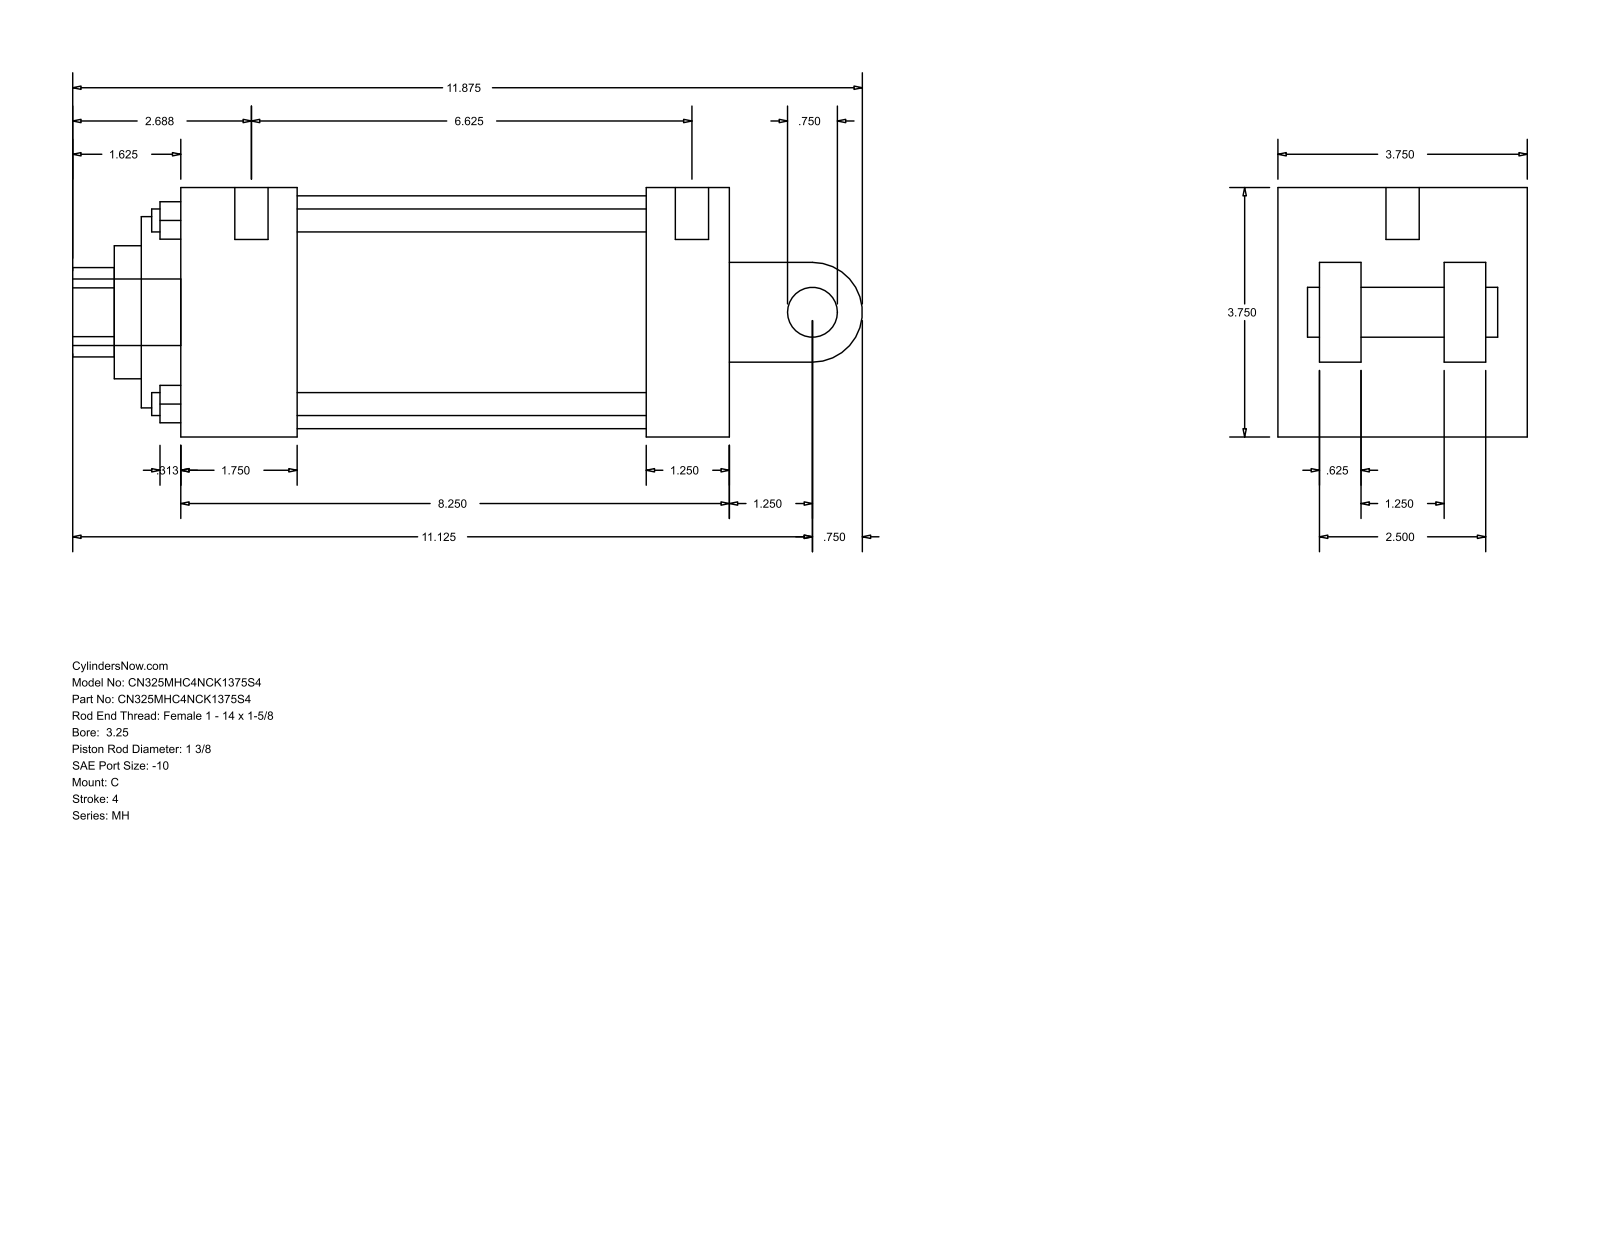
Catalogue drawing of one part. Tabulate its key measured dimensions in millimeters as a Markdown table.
| quantity | value |
| --- | --- |
| part name | MH_C__0325_1.375 |
| STEP written by | GSSL Pune (CONFIG_CONTROL_DESIGN) |
| units | millimeters |
| bodies | 0 solids, 101 faces (71 planar, 30 cylindrical, 0 other) |
| overall size | 301.62 × 95.25 × 95.25 |
| round holes (diameter × count) | 8.76 × 4, 5.56 × 2, 12.7 × 1, 34.92 × 1, 50.8 × 1, 73.03 × 1, 88.9 × 1 |
| round bosses / shafts (diameter × count) | 5.56 × 2, 25.4 × 1, 19.05 × 1, 12.7 × 1 |
| partial cylindrical surfaces (radius × count) | 17.06 × 1, 19.05 × 1 |
| main face-to-face distances | 95.24, 15.87, 209.55, 63.5, 79.37, 31.74, 47.63, 44.45, 177.8, 133.35 |
| hole center spacings | 49.57, 70.1, 99.14, 4.76 |
